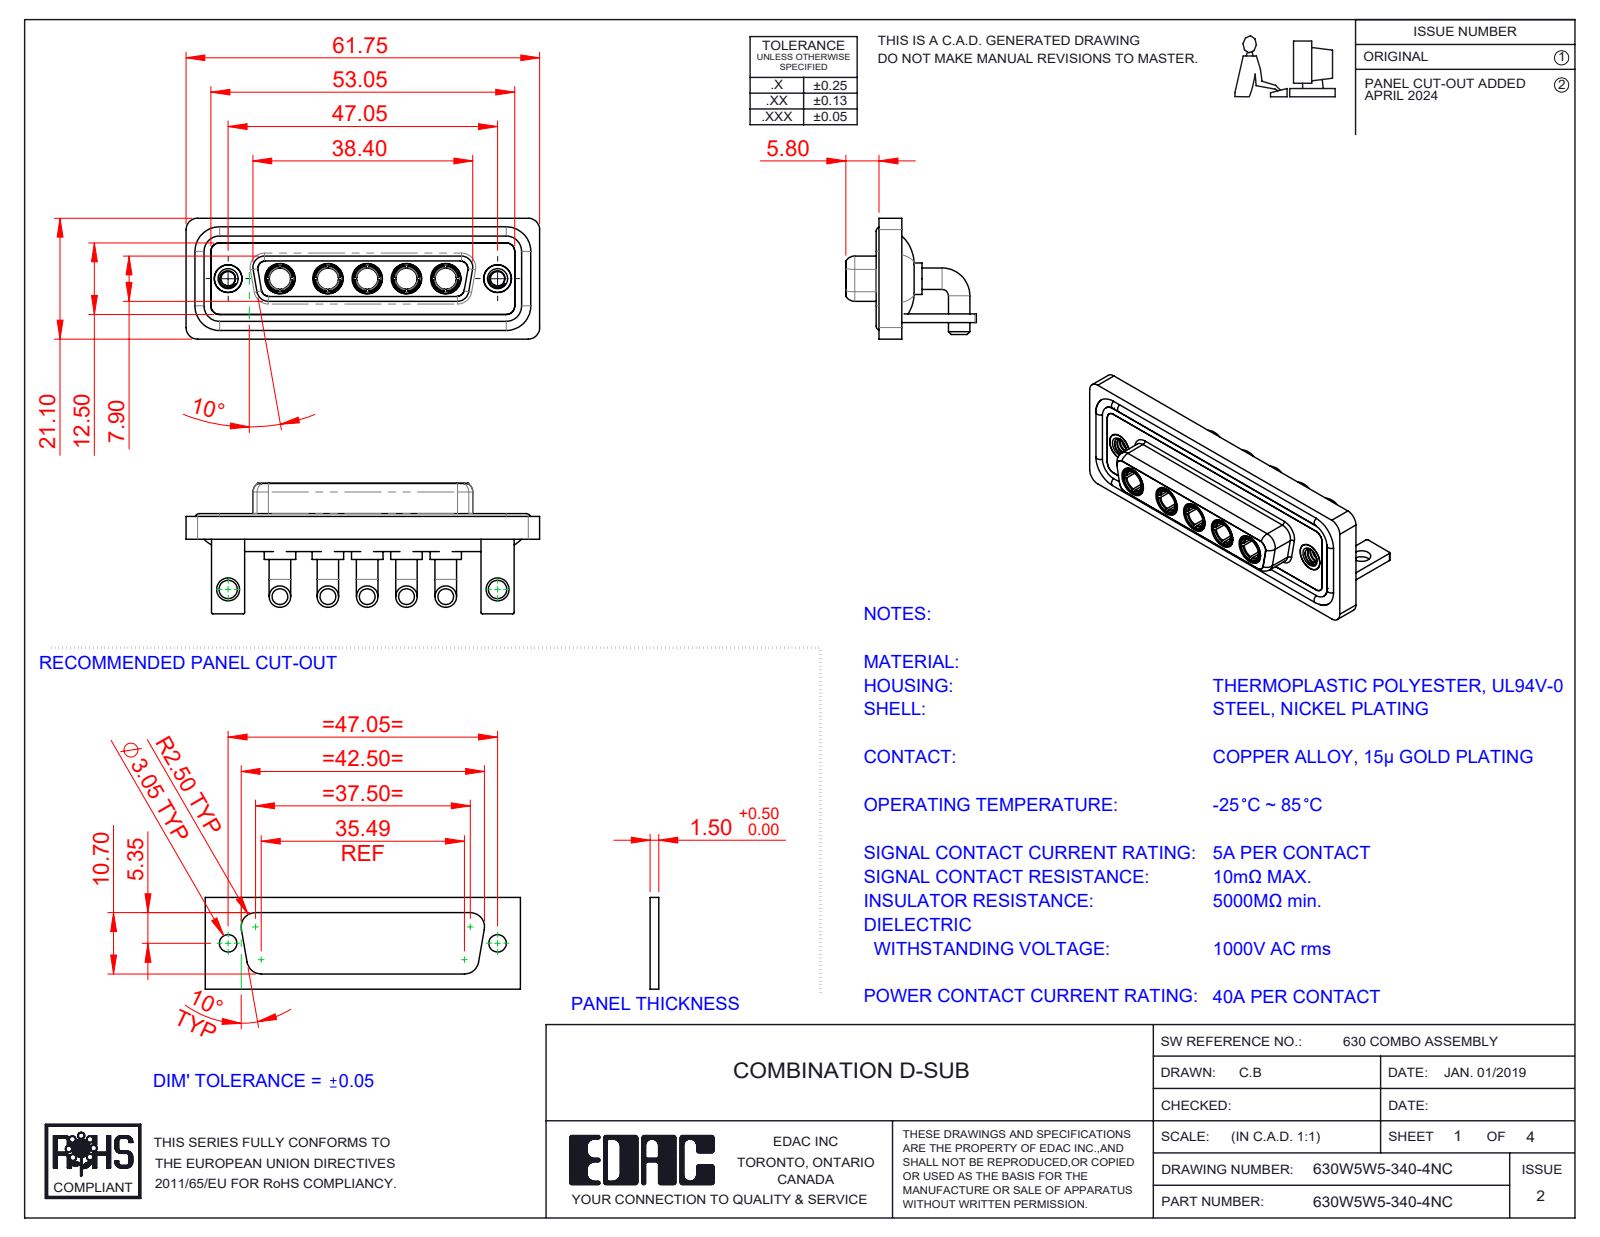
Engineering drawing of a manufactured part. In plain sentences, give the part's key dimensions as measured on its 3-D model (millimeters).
The part is named "630Combo Housing_5W5; 630Combo Shell Front_25 Contacts; 630Combo Shell Rear_25 Contacts; 630Combo Waterproof Housing_25 Contacts (+4 more)". Its 3-D file was written by "SolidWorks 2023 (CONFIG_CONTROL_DESIGN)". It is 19 solids with 818 faces: 270 planar, 335 cylindrical and 213 other. Overall it measures 61.75 by 22.8 by 21.1 millimeters. Its volume is 9 158 cubic millimeters and its surface area 14 771 square millimeters. Round holes: 7 of diameter 4.85, 5 of diameter 3.7, 5 of diameter 5.3, 2 of diameter 2.5, 2 of diameter 3.2, 2 of diameter 4, 2 of diameter 4.05, 2 of diameter 5. Round bosses or shafts: 10 of diameter 3.75, 5 of diameter 5.5, 5 of diameter 5.2, 5 of diameter 4.96, 5 of diameter 4.75, 4 of diameter 1.6, 2 of diameter 4.95, 2 of diameter 4.8. Partial cylindrical surfaces (rounded edges, fillets, slot ends): 19 of radius 2, 18 of radius 1.5, 16 of radius 0.25, 8 of radius 1.35, 8 of radius 1.6, 5 of radius 0.5, 5 of radius 2.1, 4 of radius 0.6. The main face-to-face distances are 0.4, 1.8, 2.9, 3.7, 1.5, 4.1, 1.1, 1.4, 1.6, 2.5. The hole center spacings are 6.86, 9.04, 38.01, 47.05, 6.87, 8.38, 13.72, 13.73.
